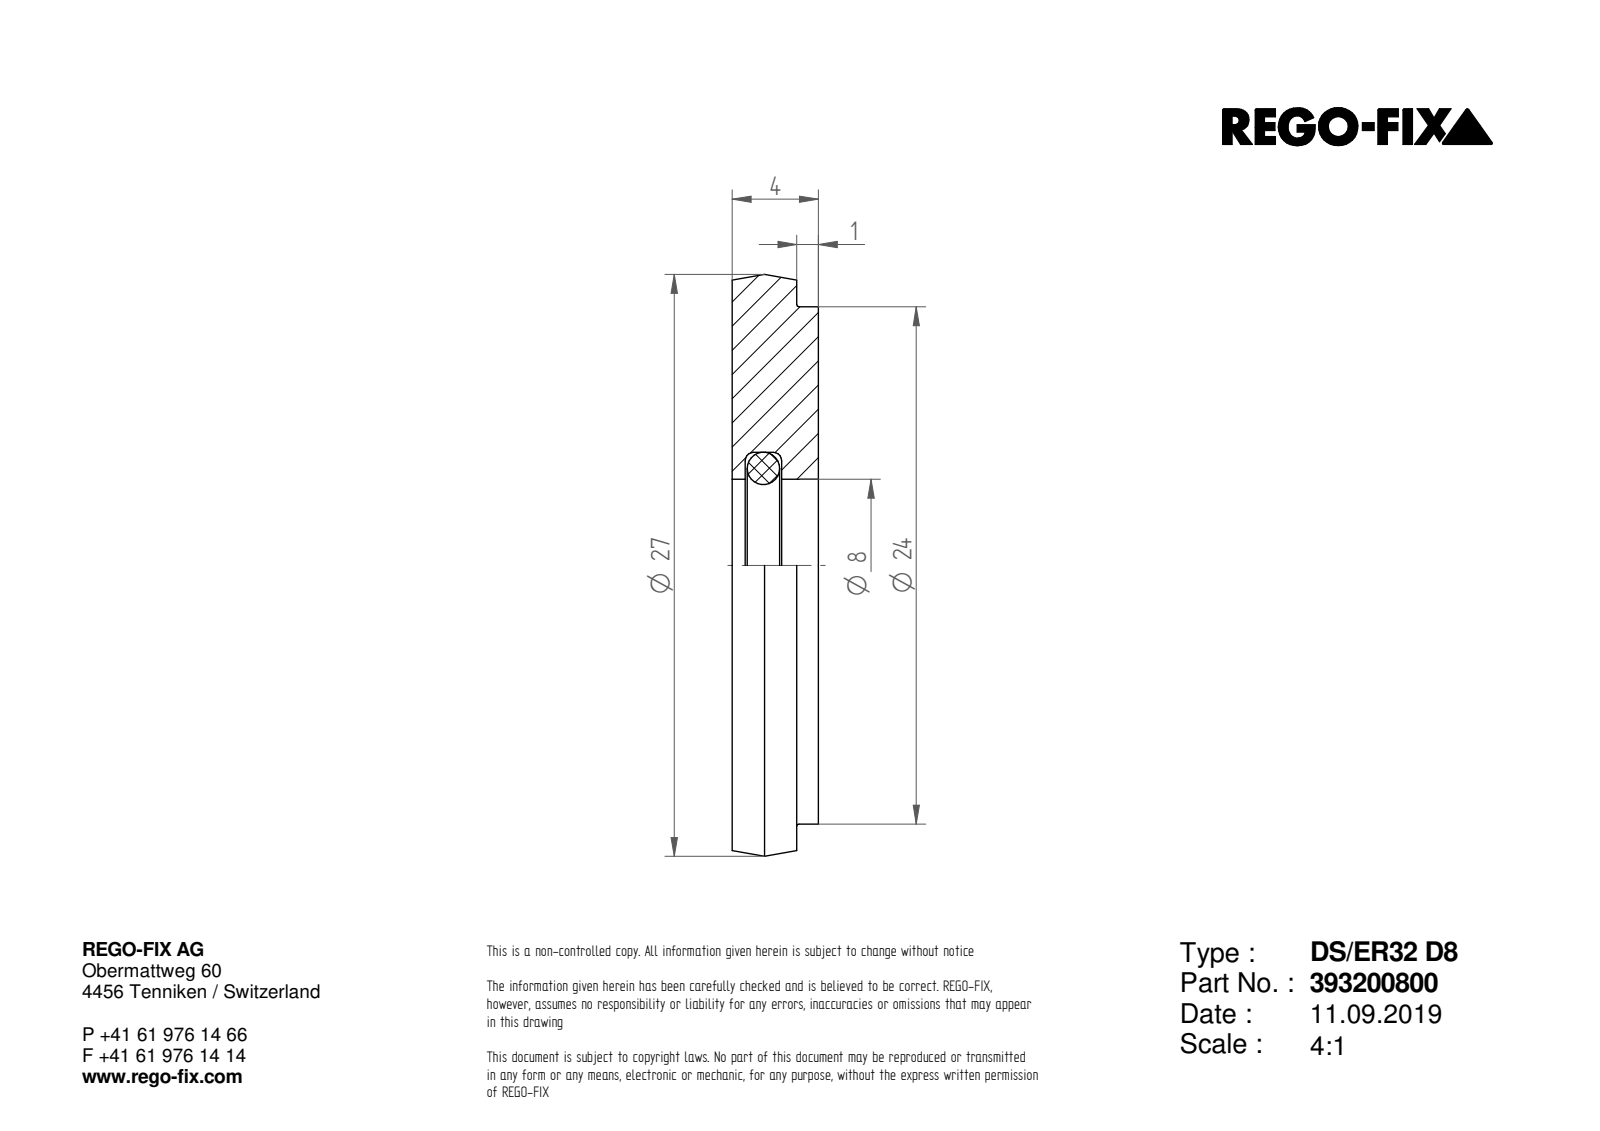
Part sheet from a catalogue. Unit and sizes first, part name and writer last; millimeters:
Units: millimetres
Overall size (bounding box): 27 × 27 × 4
Round holes (diameter × count): ⌀8 ×1
Round bosses / shafts (diameter × count): ⌀27 ×1, ⌀24 ×1
Main face-to-face distances: 4, 1, 3
Volume: 1 969 mm³ · Surface area: 1 472 mm²
Bodies: 1 solid, 7 faces (3 planar, 3 cylindrical, 1 other)
Part name (STEP PRODUCT): NOCUT
STEP written by: SIEMENS PLM Software Solid Edge ST10 (AUTOMOTIVE_DESIGN)
